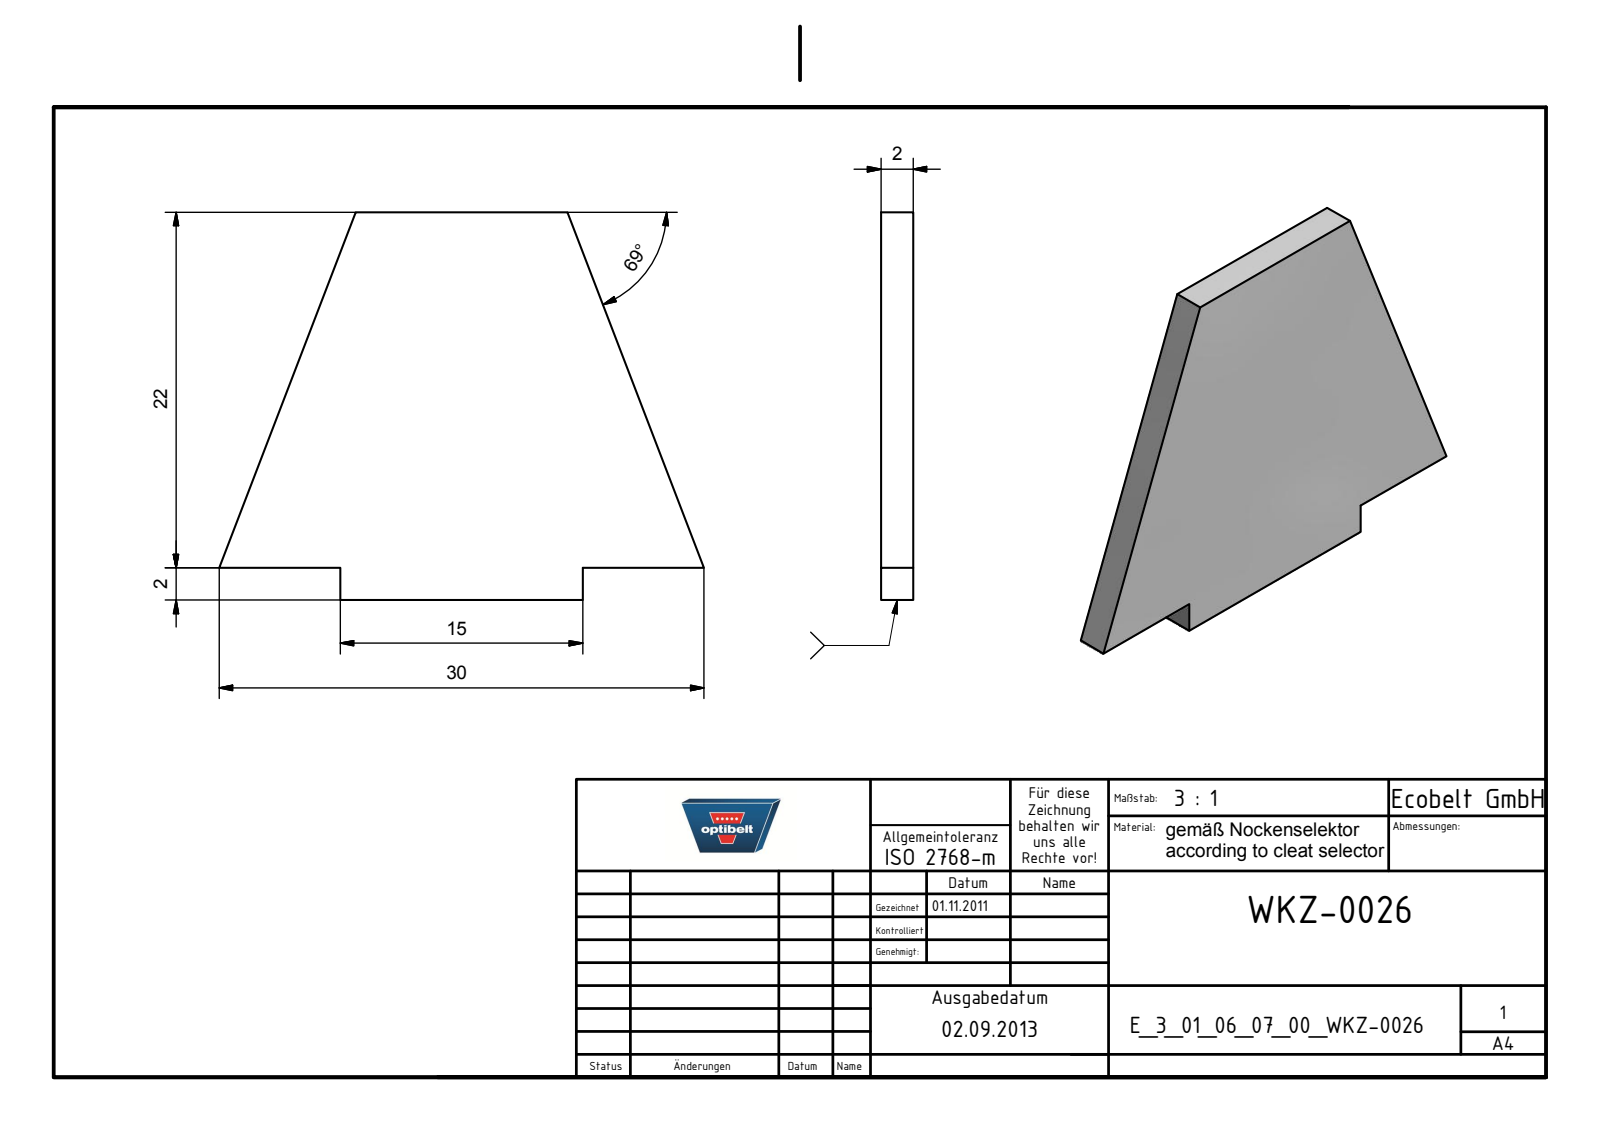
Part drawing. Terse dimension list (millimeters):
name: E_3_01_06_07_00_WKZ-0026
written by: Autodesk Inventor 2021 (AUTOMOTIVE_DESIGN)
unit: mm
bodies: 1 solid, 10 faces (10 planar, 0 cylindrical, 0 other)
size: 30 × 24 × 2
volume: 1 008 mm³; area: 1 197 mm²
face distances: 2, 24, 22, 15
